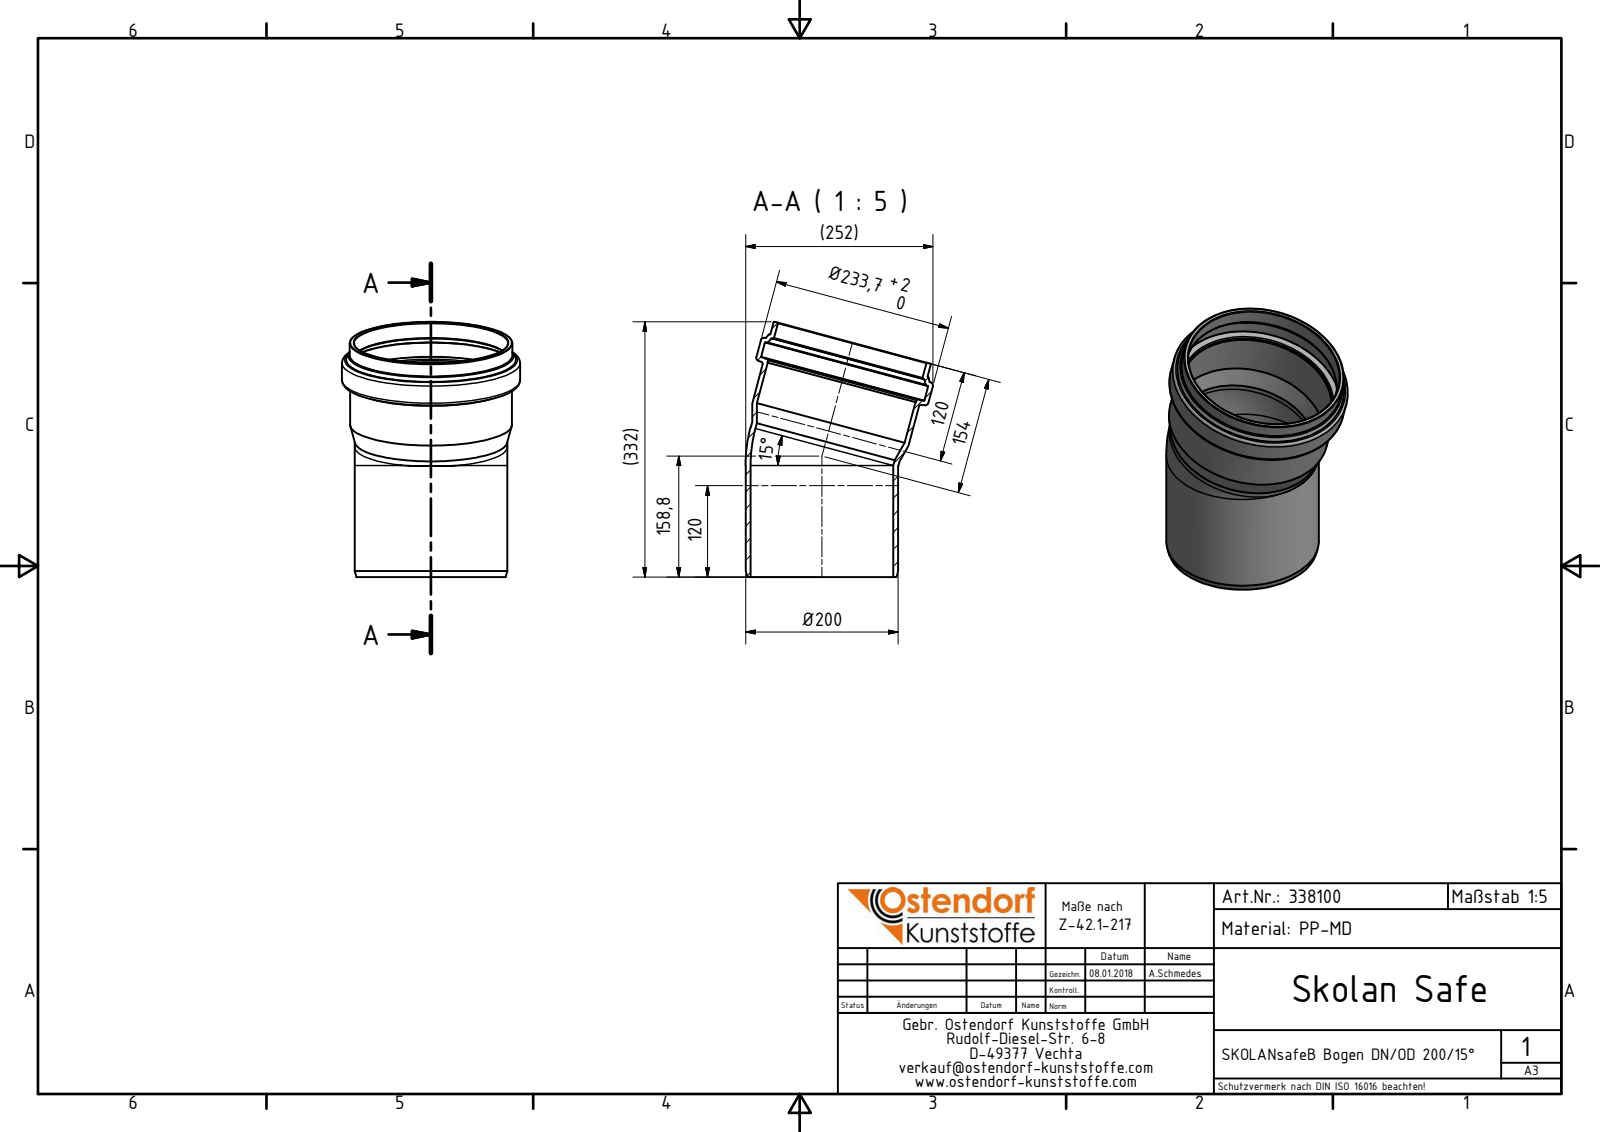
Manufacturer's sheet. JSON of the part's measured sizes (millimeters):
{"part_name": "338100 SKOLANsafeB Bogen DN_OD 200_15°", "step_written_by": "Autodesk Inventor 2016 (AUTOMOTIVE_DESIGN)", "units": "millimeters", "bodies": {"solids": 1, "faces": 41, "planar": 3, "cylindrical": 11, "other": 27}, "overall_size": [334.97, 245.84, 233.7], "volume_mm3": 1283000, "surface_area_mm2": 420416, "round_holes": [[187.2, 2], [201.8, 2], [200.8, 1], [221.9, 1]], "round_bosses_or_shafts": [[200.2, 2], [233.7, 1], [213.6, 1], [212.6, 1]], "face_to_face_distances": [53.89]}
